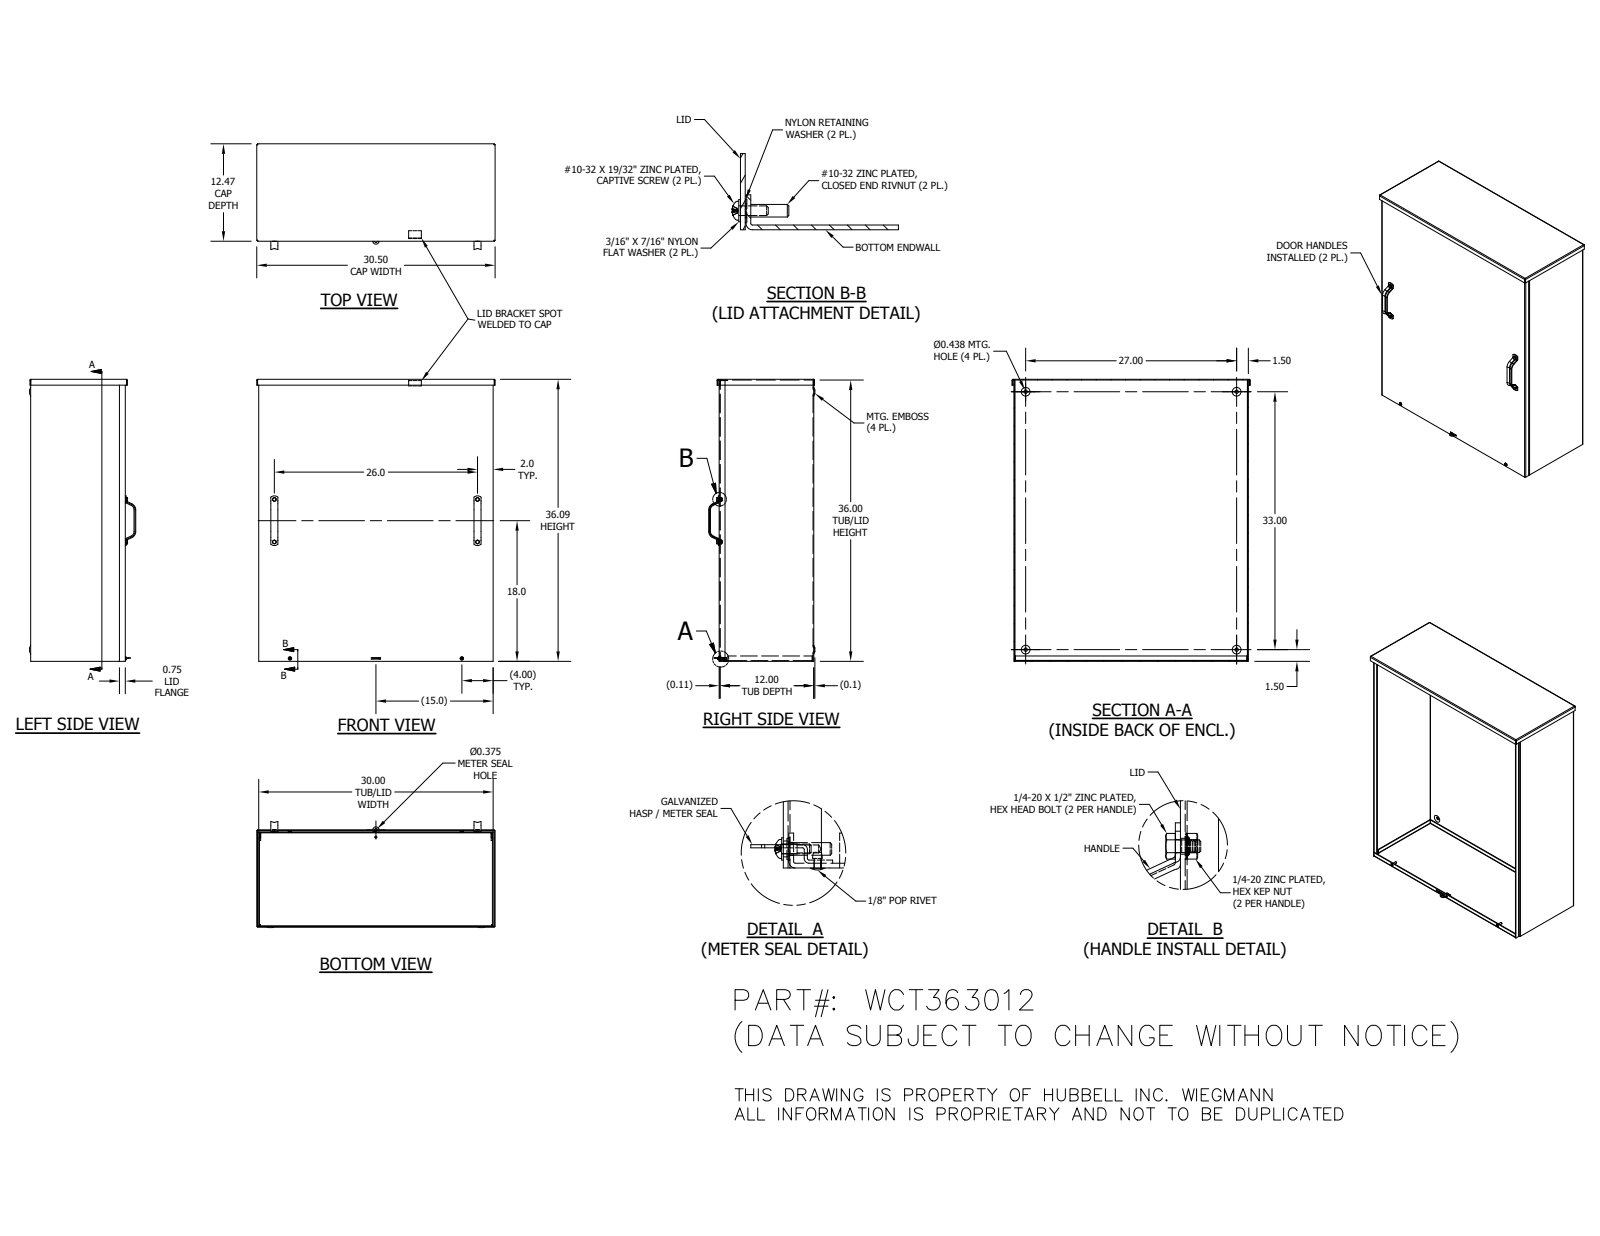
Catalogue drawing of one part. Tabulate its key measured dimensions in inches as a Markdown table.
| quantity | value |
| --- | --- |
| part name | WCT363012BKP; WCT3012BTM; WCT3630LID; WCT3012CAP (+8 more) |
| STEP written by | Autodesk Inventor 2014 (AUTOMOTIVE_DESIGN) |
| units | inches |
| bodies | 30 solids, 1094 faces (540 planar, 315 cylindrical, 239 other) |
| overall size | 36.134 × 30.5 × 13.587 |
| volume | 367.2 in³ |
| surface area | 7 899 in² |
| round holes (diameter × count) | 0.313 × 6, 0.19 × 4, 0.25 × 4, 0.289 × 4, 0.335 × 4, 0.38 × 4, 0.437 × 4, 0.125 × 2, 0.156 × 2, 0.188 × 2, 0.196 × 2, 0.257 × 2 |
| round bosses / shafts (diameter × count) | 0.438 × 4, 0.375 × 4, 0.33 × 4, 0.28 × 4, 0.453 × 2, 0.437 × 2, 0.406 × 2, 0.373 × 2 |
| partial cylindrical surfaces (radius × count) | 0.02 × 96, 0.031 × 19, 0.125 × 16, 0.05 × 8, 0.1 × 8, 0.2 × 8, 0.194 × 4, 0.696 × 4 |
| main face-to-face distances | 0.094, 12.016, 12.109, 11.922, 29.906, 36, 29.813, 30, 36.094, 35.906 |
| hole center spacings | 13.79, 19.226, 22, 24.526, 27.857, 28.252, 29.869, 31.462 |
